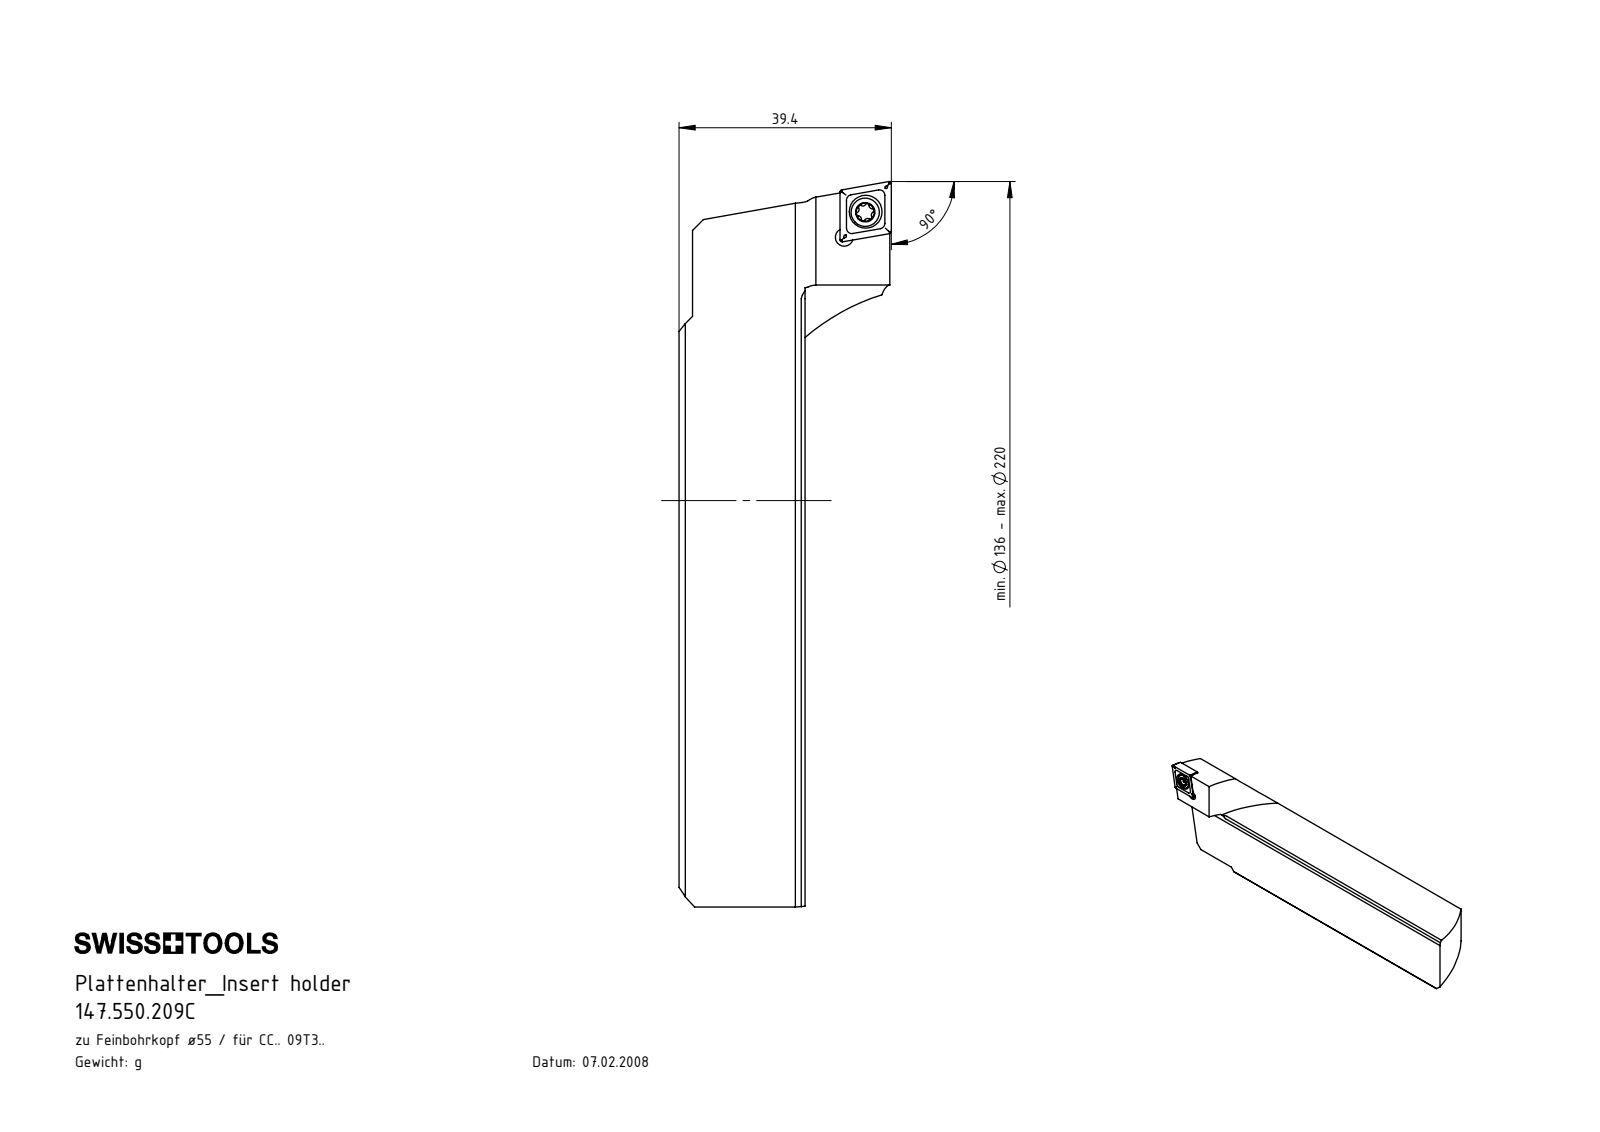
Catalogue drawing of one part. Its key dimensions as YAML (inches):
part_name: "147.550.209C; F00-WCB.136.001_C; WCB-ER2.001.009_A; CCMT09T304"
step_written_by: "SolidWorks 2017 (CONFIG_CONTROL_DESIGN)"
units: inches
bodies: {solids: 3, faces: 559, planar: 342, cylindrical: 39, other: 178}
overall_size: [5.298, 1.551, 1.077]
volume: 3.396
surface_area: 21.7
round_holes:
  - {diameter: 0.13, count: 2}
  - {diameter: 0.173, count: 1}
  - {diameter: 0.24, count: 1}
round_bosses_or_shafts:
  - {diameter: 0.207, count: 1}
  - {diameter: 0.157, count: 1}
partial_cylinders:
  - {radius: 0.008, count: 8}
  - {radius: 0.013, count: 6}
  - {radius: 0.023, count: 6}
  - {radius: 1.575, count: 3}
  - {radius: 0.031, count: 1}
face_to_face_distances: [0.094, 0.839, 0.187, 0.281, 0.375, 0.188, 0.281, 0.375, 0.469, 0.563]
hole_center_spacings: [0.239, 0.244]
